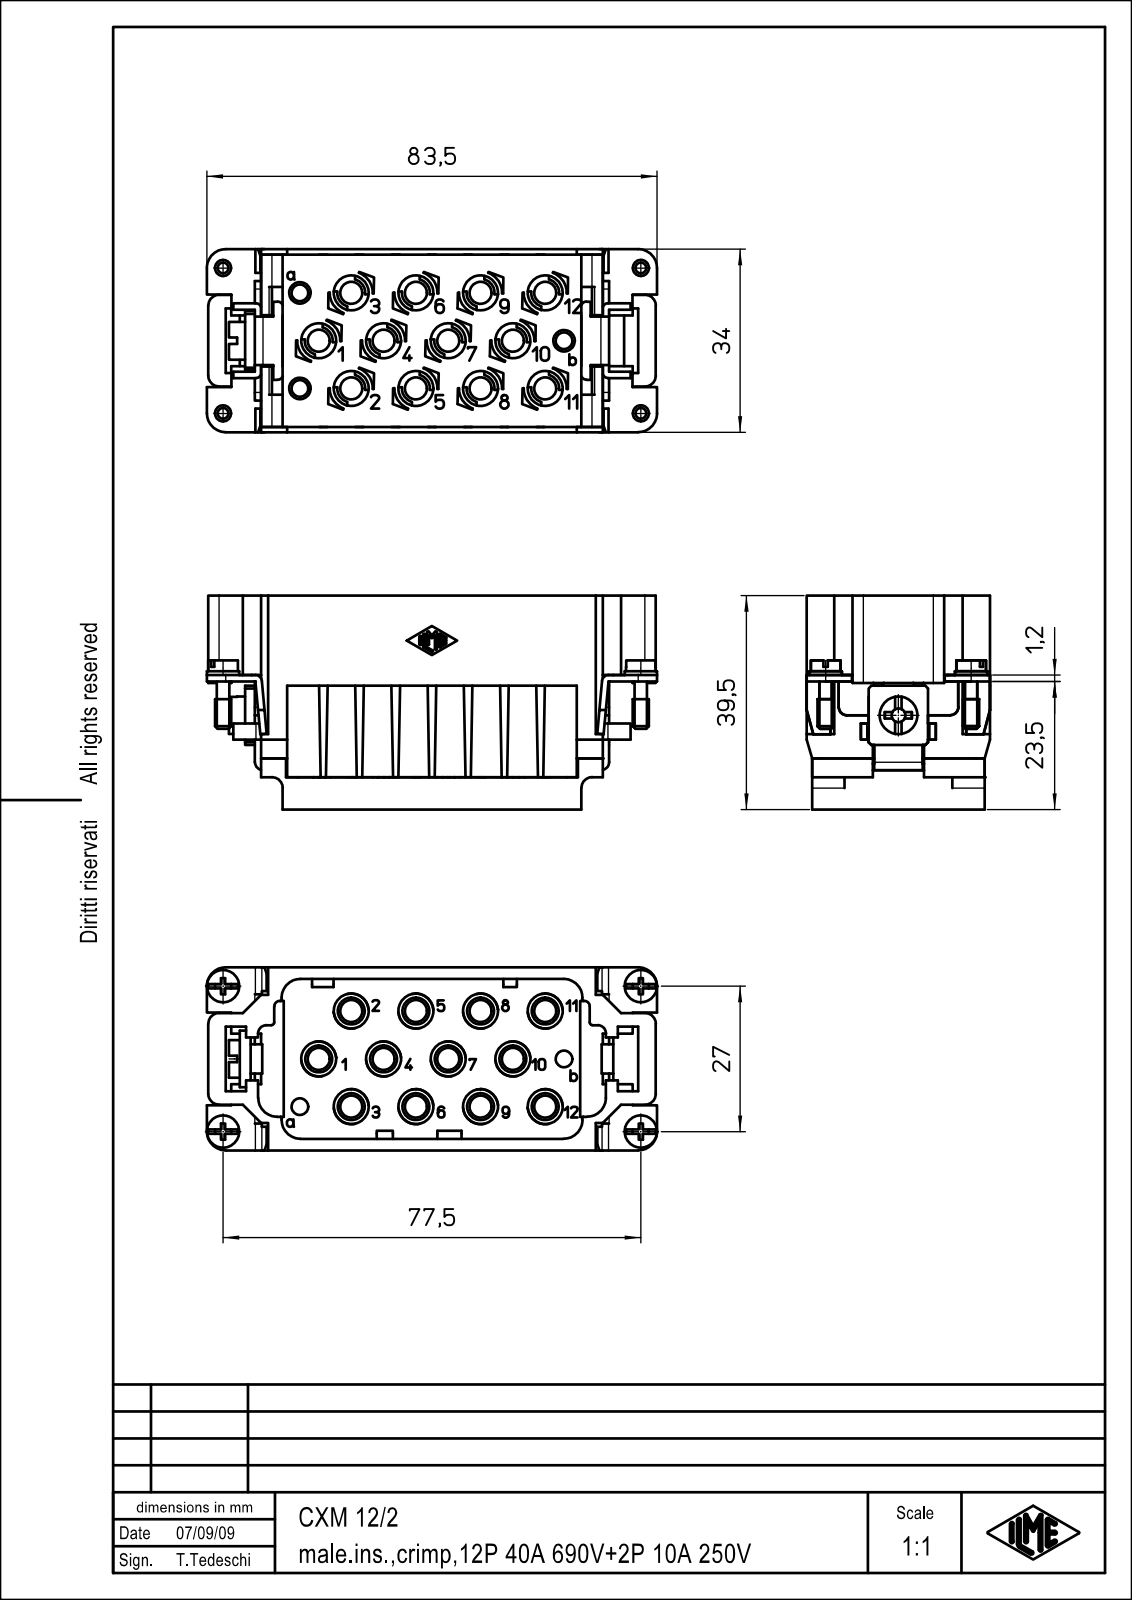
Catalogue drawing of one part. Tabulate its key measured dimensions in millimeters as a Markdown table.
| quantity | value |
| --- | --- |
| part name | CXM 12_2 |
| STEP written by | Autodesk Inventor 7 (AUTOMOTIVE_DESIGN) |
| units | millimeters |
| bodies | 1 solid, 1122 faces (510 planar, 114 cylindrical, 498 other) |
| overall size | 83.5 × 39.5 × 34 |
| volume | 48 778 mm³ |
| surface area | 28 905 mm² |
| round holes (diameter × count) | 4 × 12, 6.4 × 12, 3.24 × 1 |
| round bosses / shafts (diameter × count) | 5.5 × 2, 5.3 × 2, 3 × 2, 2.6 × 2, 7 × 1 |
| partial cylindrical surfaces (radius × count) | 0.1 × 14, 2 × 6, 3 × 4, 3.5 × 4, 0.5 × 2, 1 × 2, 5.5 × 1 |
| main face-to-face distances | 1, 2, 31, 32, 24.5, 34, 30, 3, 33, 29 |
| hole center spacings | 10.72, 20.07, 12, 21.43, 24, 31.29, 17.76, 29.86 |
